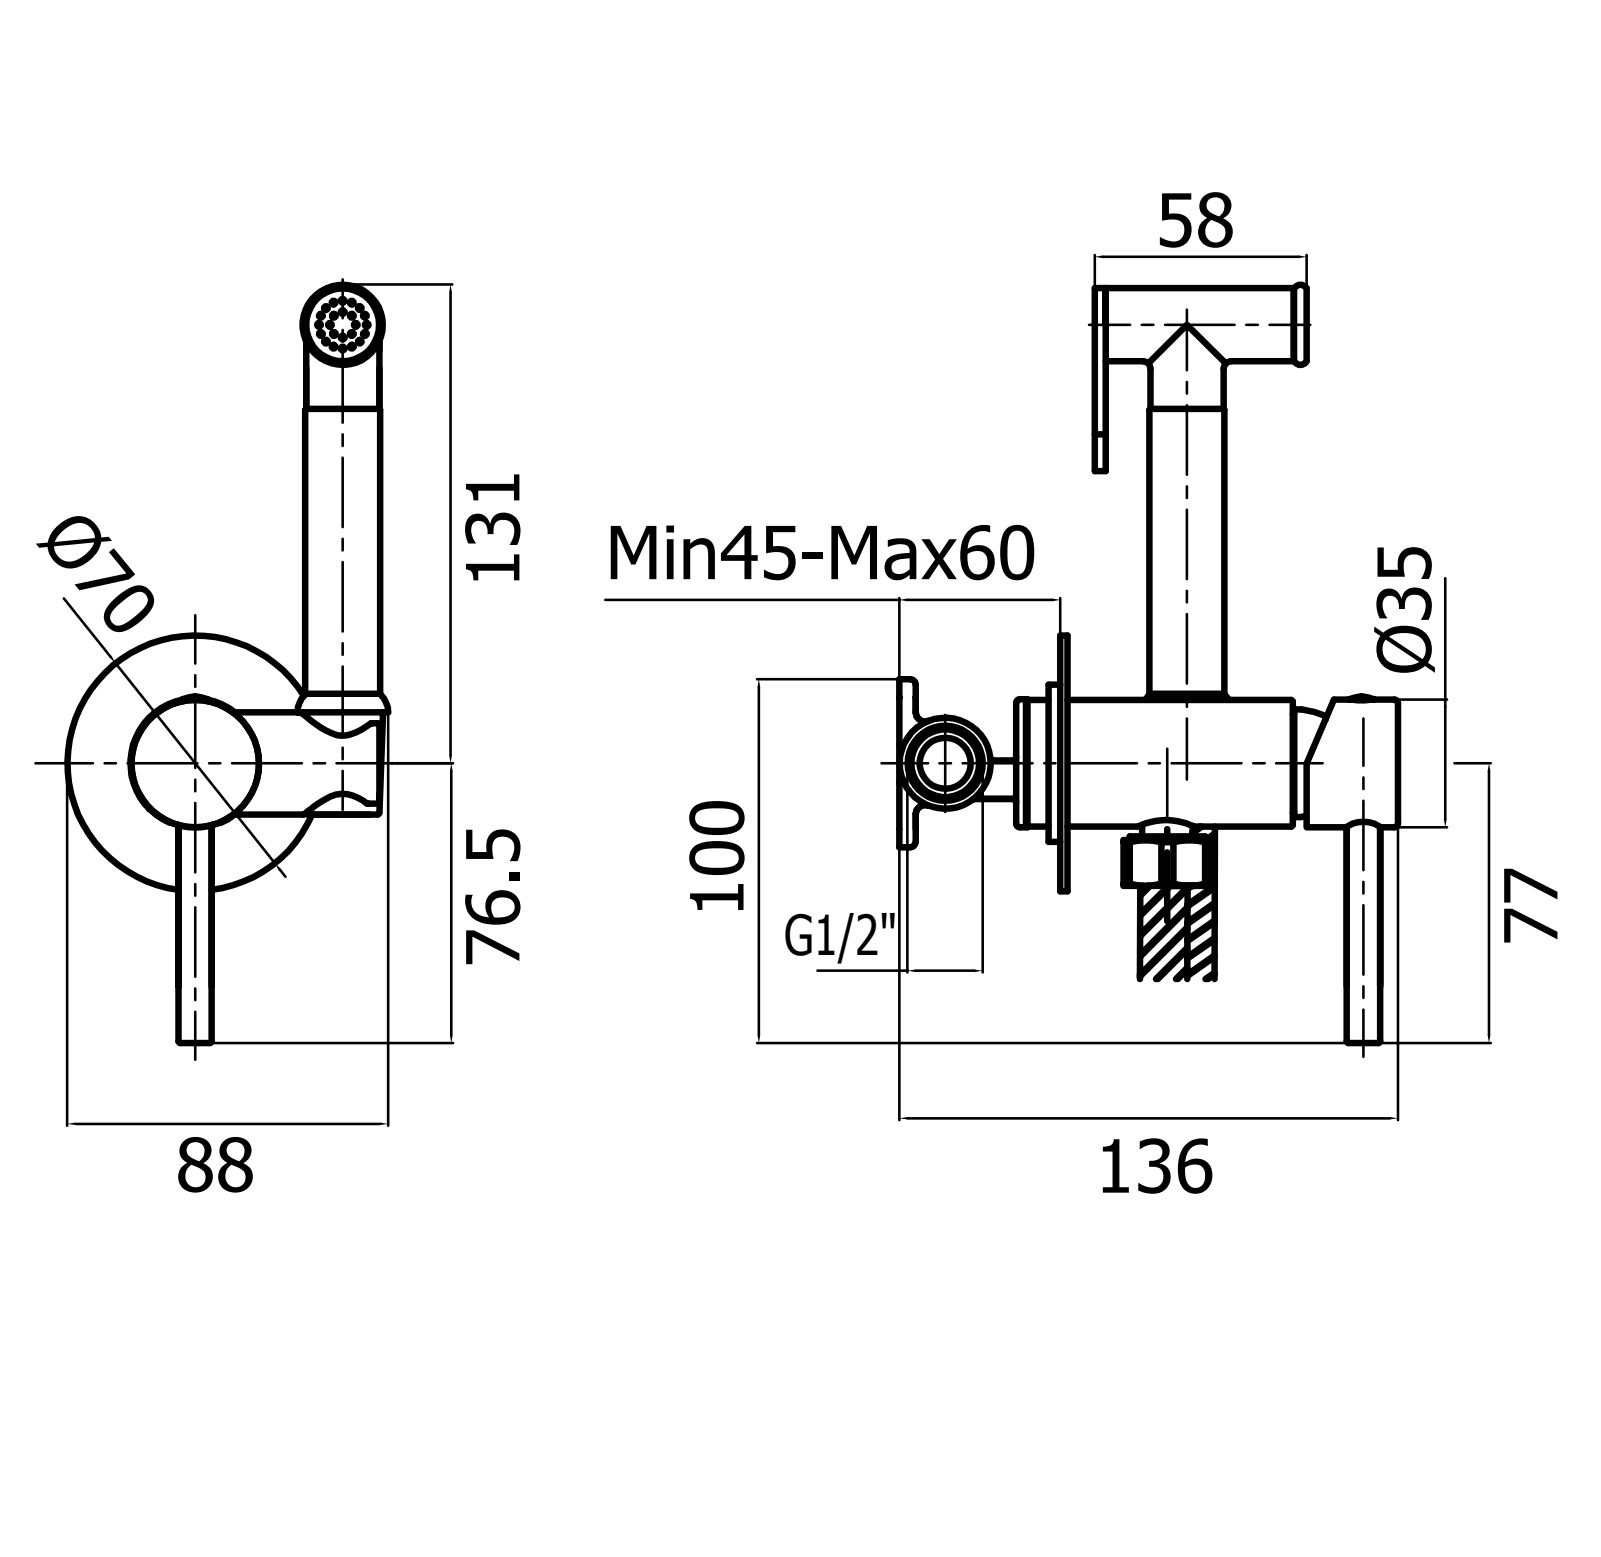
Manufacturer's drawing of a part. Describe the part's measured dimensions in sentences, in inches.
The part is named "TOM2CB481419LE2_1_AF0; TOM2CB481419LE2_5; TOM2CB481419LE2_6_AF0; TOM2CB481419LE2_7 (+8 more)". Its 3-D file was written by "CREO PARAMETRIC BY PTC INC, 2022164 (CONFIG_CONTROL_DESIGN)". It is 25 solids with 1331 faces: 233 planar, 566 cylindrical and 532 other. Overall it measures 17.094 by 4.483 by 3.708 inches. Its volume is 11.67 cubic inches and its surface area 194.3 square inches. Round holes: 24 of diameter 0.039, 8 of diameter 0.315, 3 of diameter 0.098, 3 of diameter 0.165, 3 of diameter 0.181, 3 of diameter 0.433, 3 of diameter 0.472, 2 of diameter 0.142, 2 of diameter 0.492, 2 of diameter 0.866, 1 of diameter 0.079, 1 of diameter 0.118. Round bosses or shafts: 3 of diameter 0.709, 3 of diameter 0.472, 2 of diameter 0.811, 2 of diameter 0.787, 2 of diameter 0.63, 2 of diameter 0.591, 2 of diameter 0.433, 2 of diameter 0.197. Partial cylindrical surfaces (rounded edges, fillets, slot ends): 46 of radius 0.039, 32 of radius 0.02, 8 of radius 0.118, 6 of radius 0.059, 4 of radius 0.012, 4 of radius 0.079, 2 of radius 0.102, 2 of radius 0.177. The main face-to-face distances are 0.079, 3.68, 3.758, 1.495, 1.417, 2.263, 0.118, 3.386, 1.123, 0.293. The hole center spacings are 0.256, 0.473, 0.502, 0.256, 0.426, 0.256, 0.24, 0.284.
